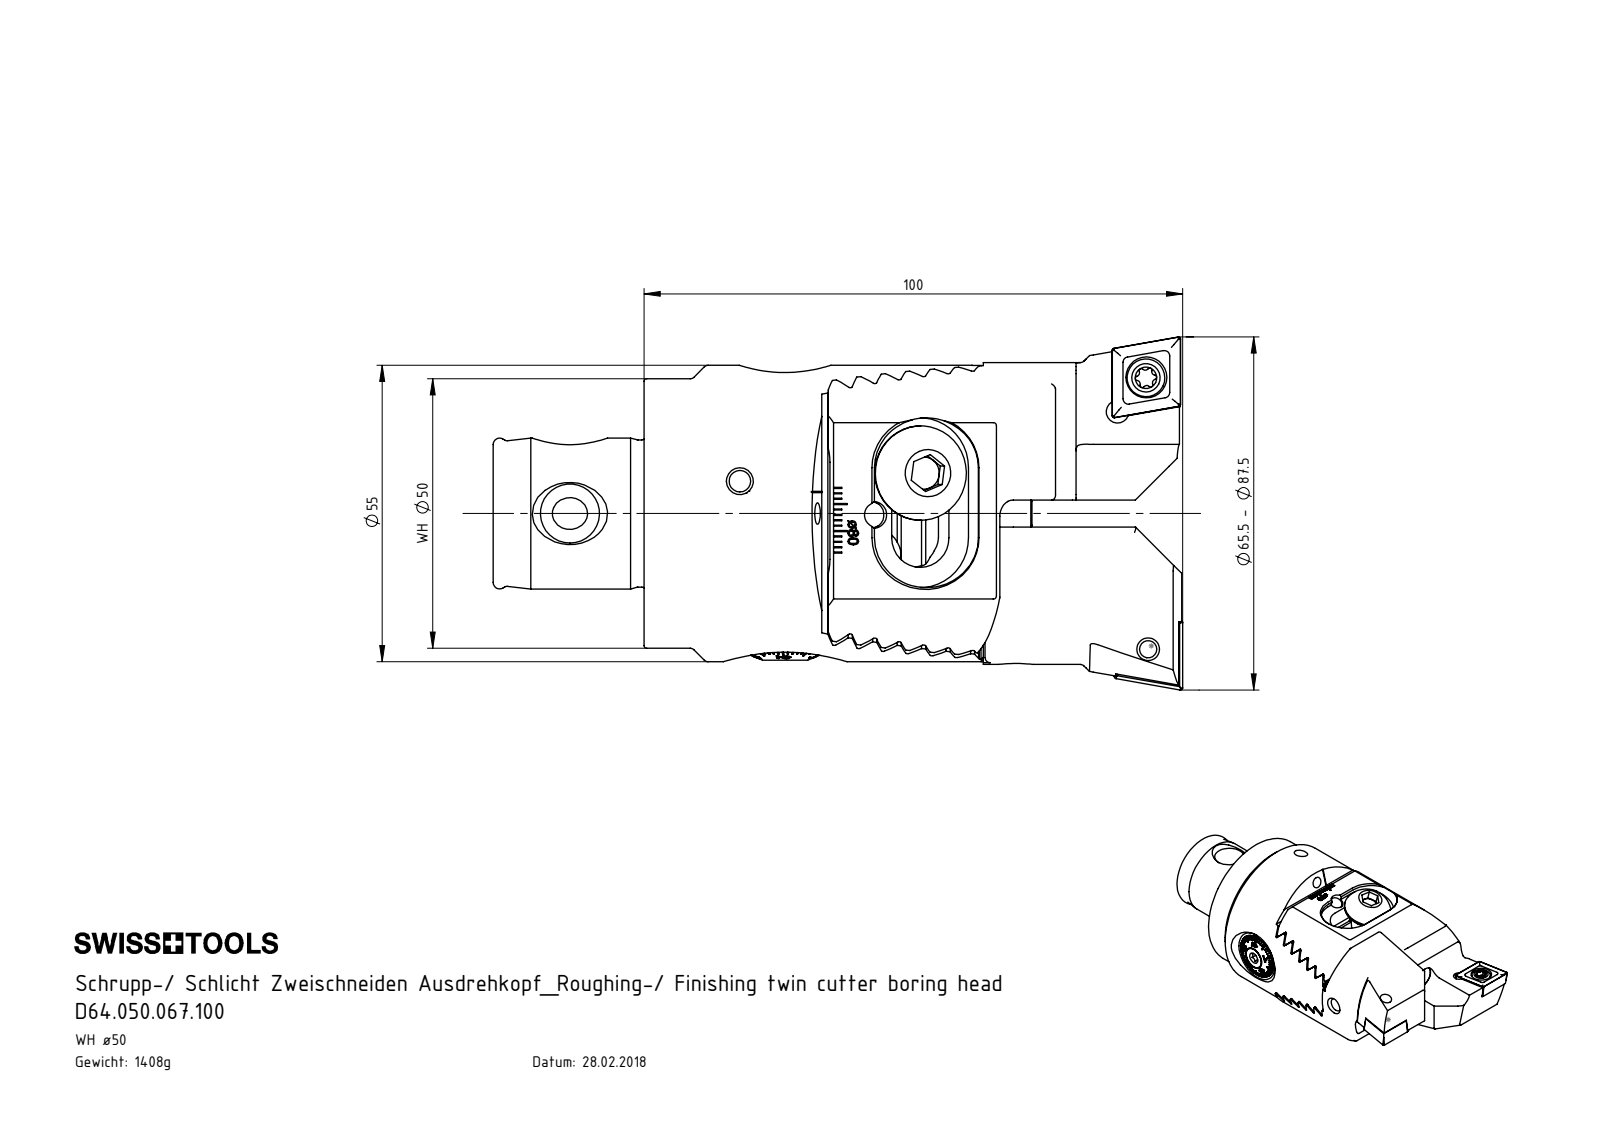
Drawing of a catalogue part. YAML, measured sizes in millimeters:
part_name: "ZC5-BG3.005.032_A_ZC5; D64.050.067.100; ZCx-BG2.00x.0xx_A_ZC5; ZC5-BG1.017.037 (+8 more)"
step_written_by: "SolidWorks 2017 (CONFIG_CONTROL_DESIGN)"
units: millimeters
bodies: {solids: 22, faces: 1508, planar: 731, cylindrical: 281, other: 496}
overall_size: [128, 65.5, 55]
volume: 180192
surface_area: 57633
round_holes:
  - {diameter: 4.2, count: 5}
  - {diameter: 5, count: 4}
  - {diameter: 8.5, count: 4}
  - {diameter: 2, count: 2}
  - {diameter: 3, count: 2}
  - {diameter: 4, count: 2}
  - {diameter: 5.5, count: 2}
  - {diameter: 7.6, count: 2}
  - {diameter: 10.5, count: 2}
  - {diameter: 11, count: 2}
  - {diameter: 2.5, count: 1}
  - {diameter: 2.9, count: 1}
round_bosses_or_shafts:
  - {diameter: 5, count: 4}
  - {diameter: 17, count: 3}
  - {diameter: 10, count: 3}
  - {diameter: 17.5, count: 2}
  - {diameter: 7, count: 2}
  - {diameter: 4, count: 2}
  - {diameter: 55, count: 1}
  - {diameter: 50, count: 1}
partial_cylinders:
  - {radius: 0.34, count: 14}
  - {radius: 1, count: 14}
  - {radius: 0.34, count: 12}
  - {radius: 0.39, count: 12}
  - {radius: 0.69, count: 6}
  - {radius: 0.69, count: 6}
  - {radius: 3, count: 4}
  - {radius: 5.5, count: 4}
face_to_face_distances: [4.07, 8.14, 12.21, 16.28, 4.11, 20.35, 4.03, 8.18, 4.01, 7.85]
hole_center_spacings: [44.41, 44.51, 50.43, 8.08, 8.2, 8.21, 8.33, 8.75]
